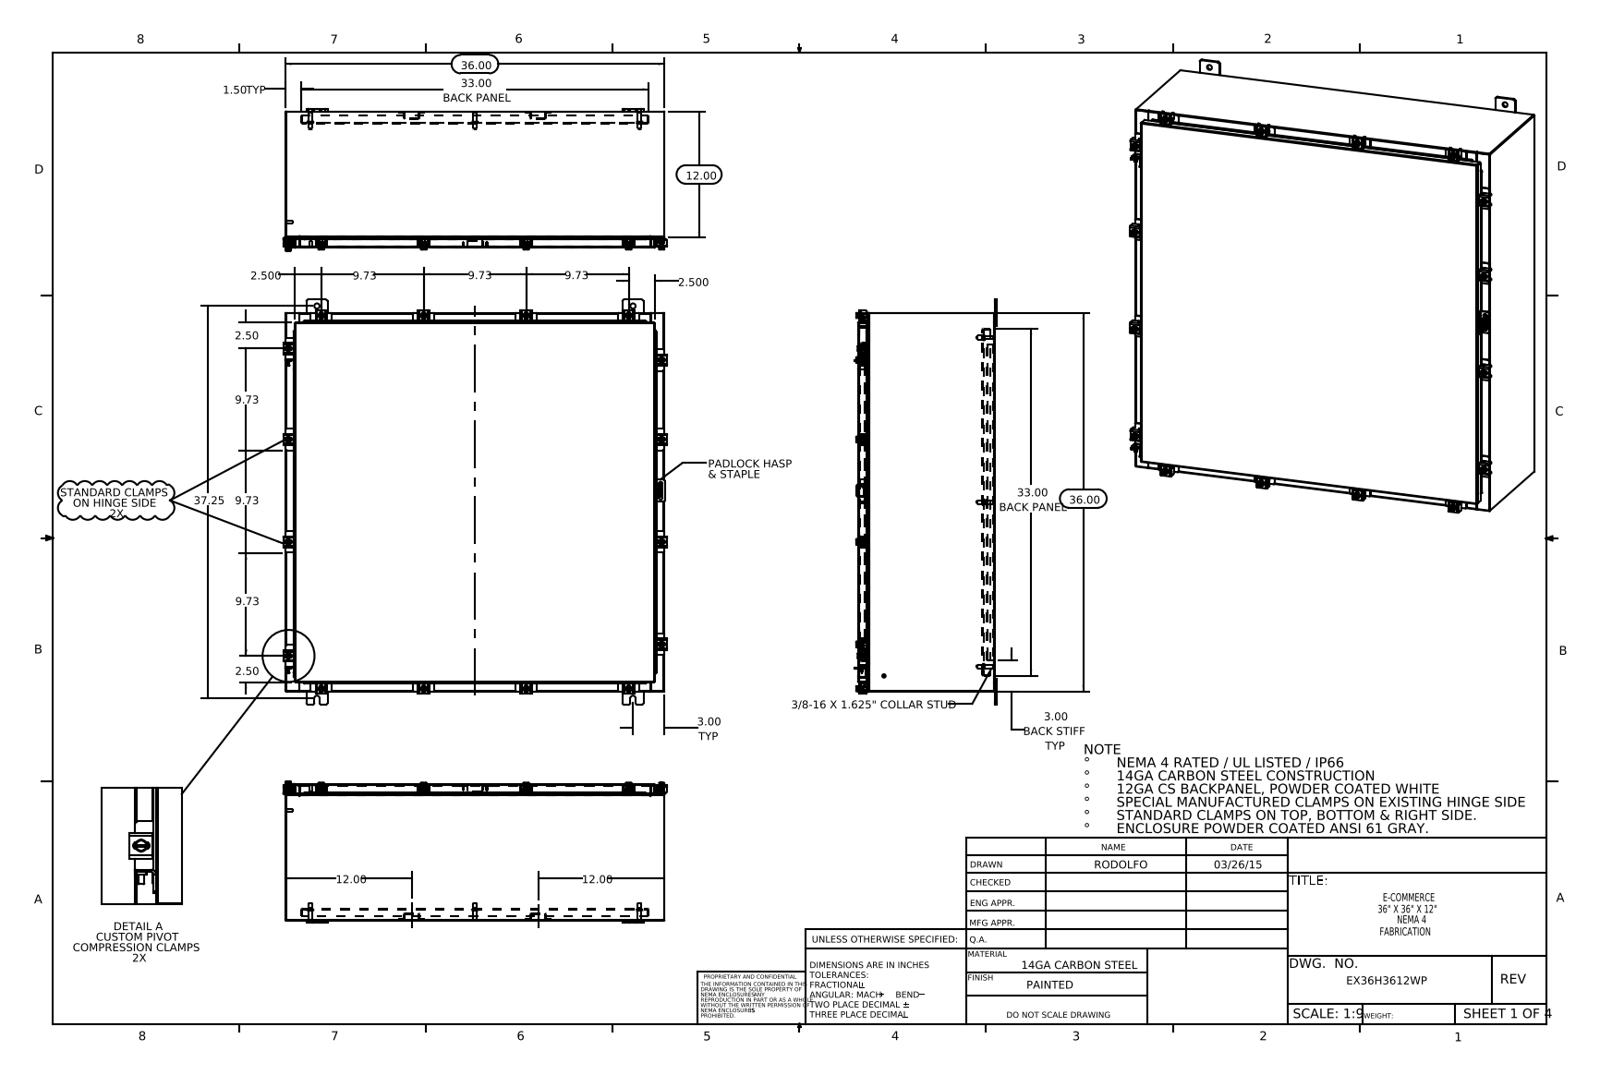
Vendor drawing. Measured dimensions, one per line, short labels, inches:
name: Quarter-20 CD Stud; EX36H3612WP Cover; N-WMT04X30402202210-00 Clamp Top; EX36H3612WP Door Stiffener (+8 more)
written by: SolidWorks 2014 (CONFIG_CONTROL_DESIGN)
unit: in
bodies: 114 solids, 2822 faces (1459 planar, 1083 cylindrical, 280 other)
size: 38.5 × 36.421 × 13.453
volume: 504.6 in³; area: 12 594 in²
holes: 16× ⌀0.213, 16× ⌀0.26, 12× ⌀0.5, 7× ⌀0.25, 1× ⌀0.125
bosses: 16× ⌀0.5, 16× ⌀0.25, 14× ⌀0.399, 8× ⌀0.625, 8× ⌀0.375, 8× ⌀0.33, 6× ⌀0.157, 6× ⌀0.14
rounds: 70× R0.06, 38× R0.013, 34× R0.088, 32× R0.141, 30× R0.12, 24× R0.19, 22× R0.09, 21× R0.05
face distances: 0.075, 12.9, 35.925, 12.826, 12.975, 0.104, 1, 1.075, 11.826, 11.9
hole spacings: 2.34, 14.744, 15.625, 17.756, 1.969, 5.288, 5.299, 7.043
